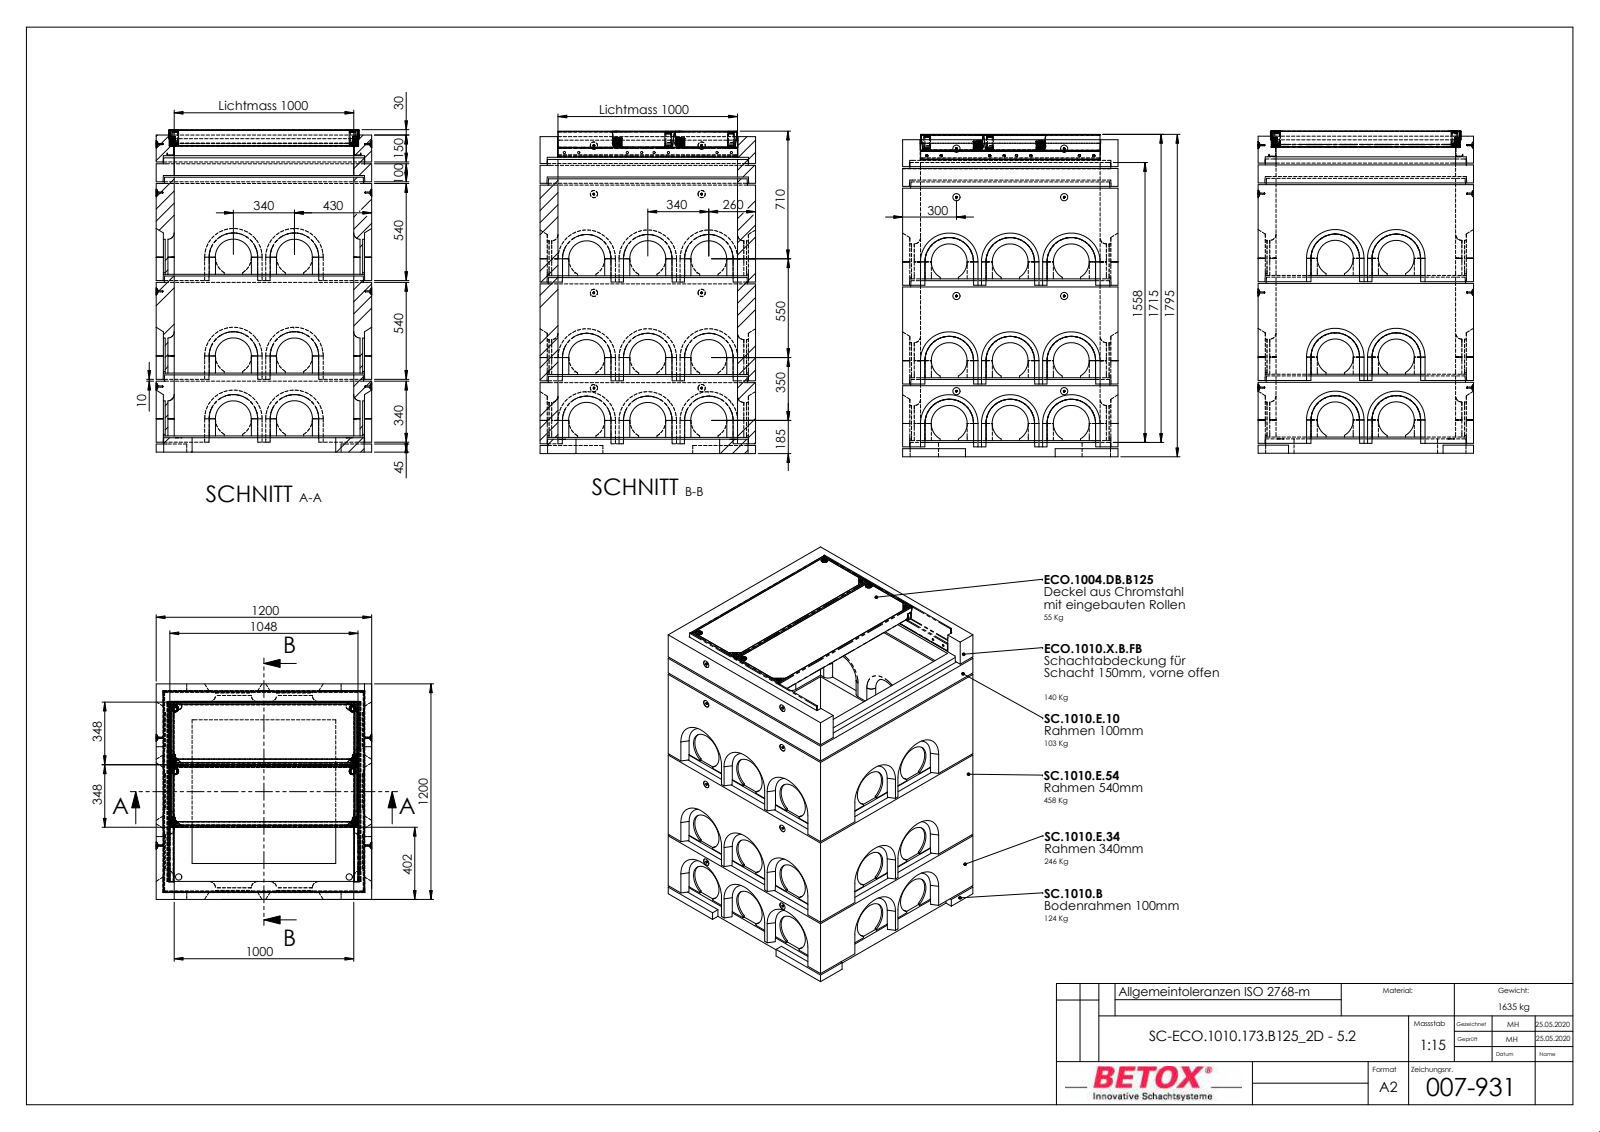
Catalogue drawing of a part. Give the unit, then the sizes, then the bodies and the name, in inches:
Units: inches
Overall size (bounding box): 71.422 × 47.244 × 47.244
Round holes (diameter × count): ⌀7.874 ×15, ⌀1.043 ×4, ⌀1.378 ×4, ⌀0.48 ×3, ⌀1.575 ×2
Round bosses / shafts (diameter × count): ⌀0.229 ×8, ⌀0.394 ×6, ⌀1.969 ×2
Partial cylindrical surfaces — rounded edges, fillets, slot ends (radius × count): R1.378 ×20, R0.118 ×9, R0.098 ×7, R0.157 ×4, R0.531 ×4, R0.079 ×2
Main face-to-face distances: 43.307, 3.937, 47.244, 39.37, 1.969, 1.378, 0.394, 0.984, 21.654, 44.685
Hole centre spacings: 13.386, 19.211, 25.457, 37.877, 13.78, 21.654, 35.433, 26.772
Bodies: 0 solids, 680 faces (439 planar, 159 cylindrical, 82 other)
Part name (STEP PRODUCT): SC-ECO.1010.173.B125_2D - 5.2
STEP written by: SolidWorks 2018 (AUTOMOTIVE_DESIGN)
